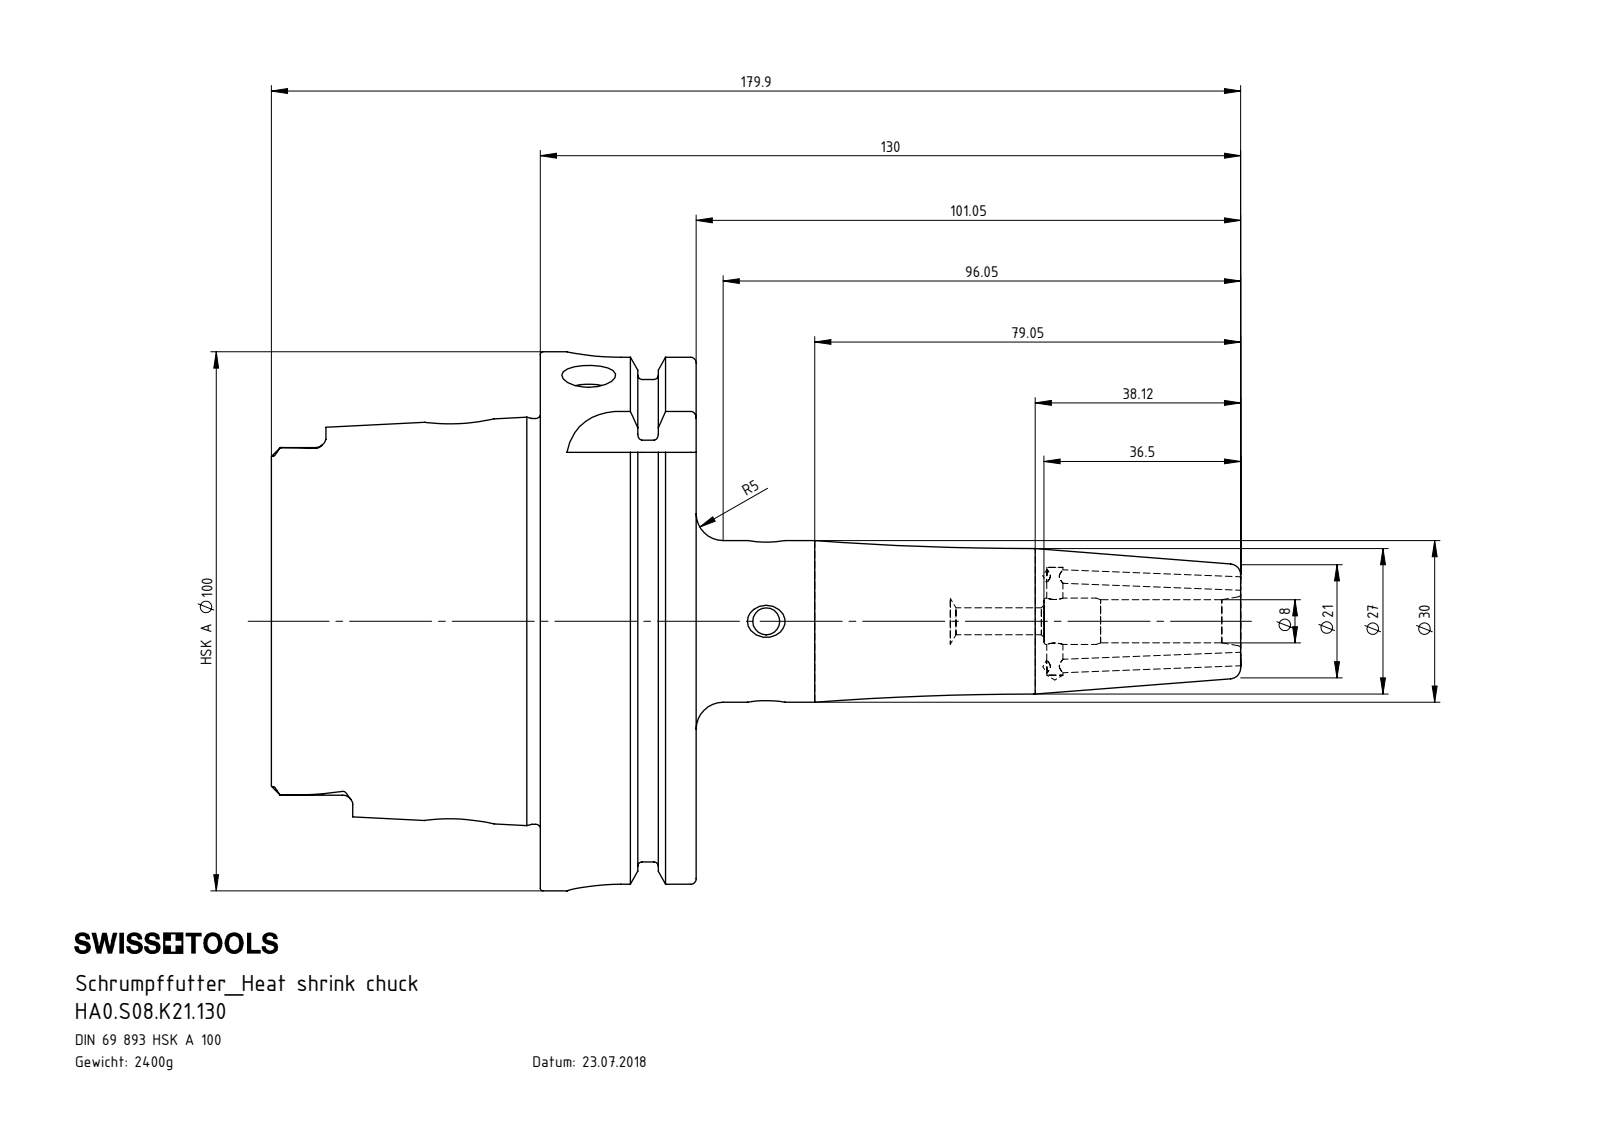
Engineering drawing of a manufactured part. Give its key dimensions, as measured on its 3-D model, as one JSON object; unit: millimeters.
{"part_name": "HA0-S08.K21.130_C_Fertigbearbeitung; ERU-AN2.K01.016_A; ERU-CJ2.001.006; HA0.S08.K21.130", "step_written_by": "SolidWorks 2017 (CONFIG_CONTROL_DESIGN)", "units": "millimeters", "bodies": {"solids": 4, "faces": 303, "planar": 95, "cylindrical": 88, "other": 120}, "overall_size": [179.98, 100, 100], "volume_mm3": 305733, "surface_area_mm2": 61989, "round_holes": [[5, 3], [10, 3], [2.5, 2], [3, 2], [8, 1], [8.5, 1], [8.6, 1], [12, 1], [22.5, 1], [26, 1], [53, 1], [63, 1]], "round_bosses_or_shafts": [[3, 2], [100, 1], [91.95, 1], [75.26, 1], [30, 1], [27, 1], [6, 1]], "partial_cylinders_radius": [[1.9, 6], [4.88, 4], [10, 4]], "face_to_face_distances": [28.95, 12.45, 16.5, 49.9, 62.35, 78.85, 78.2, 28.3, 15.85, 0.65], "hole_center_spacings": [34.95, 53.55, 56.95, 110.5]}
